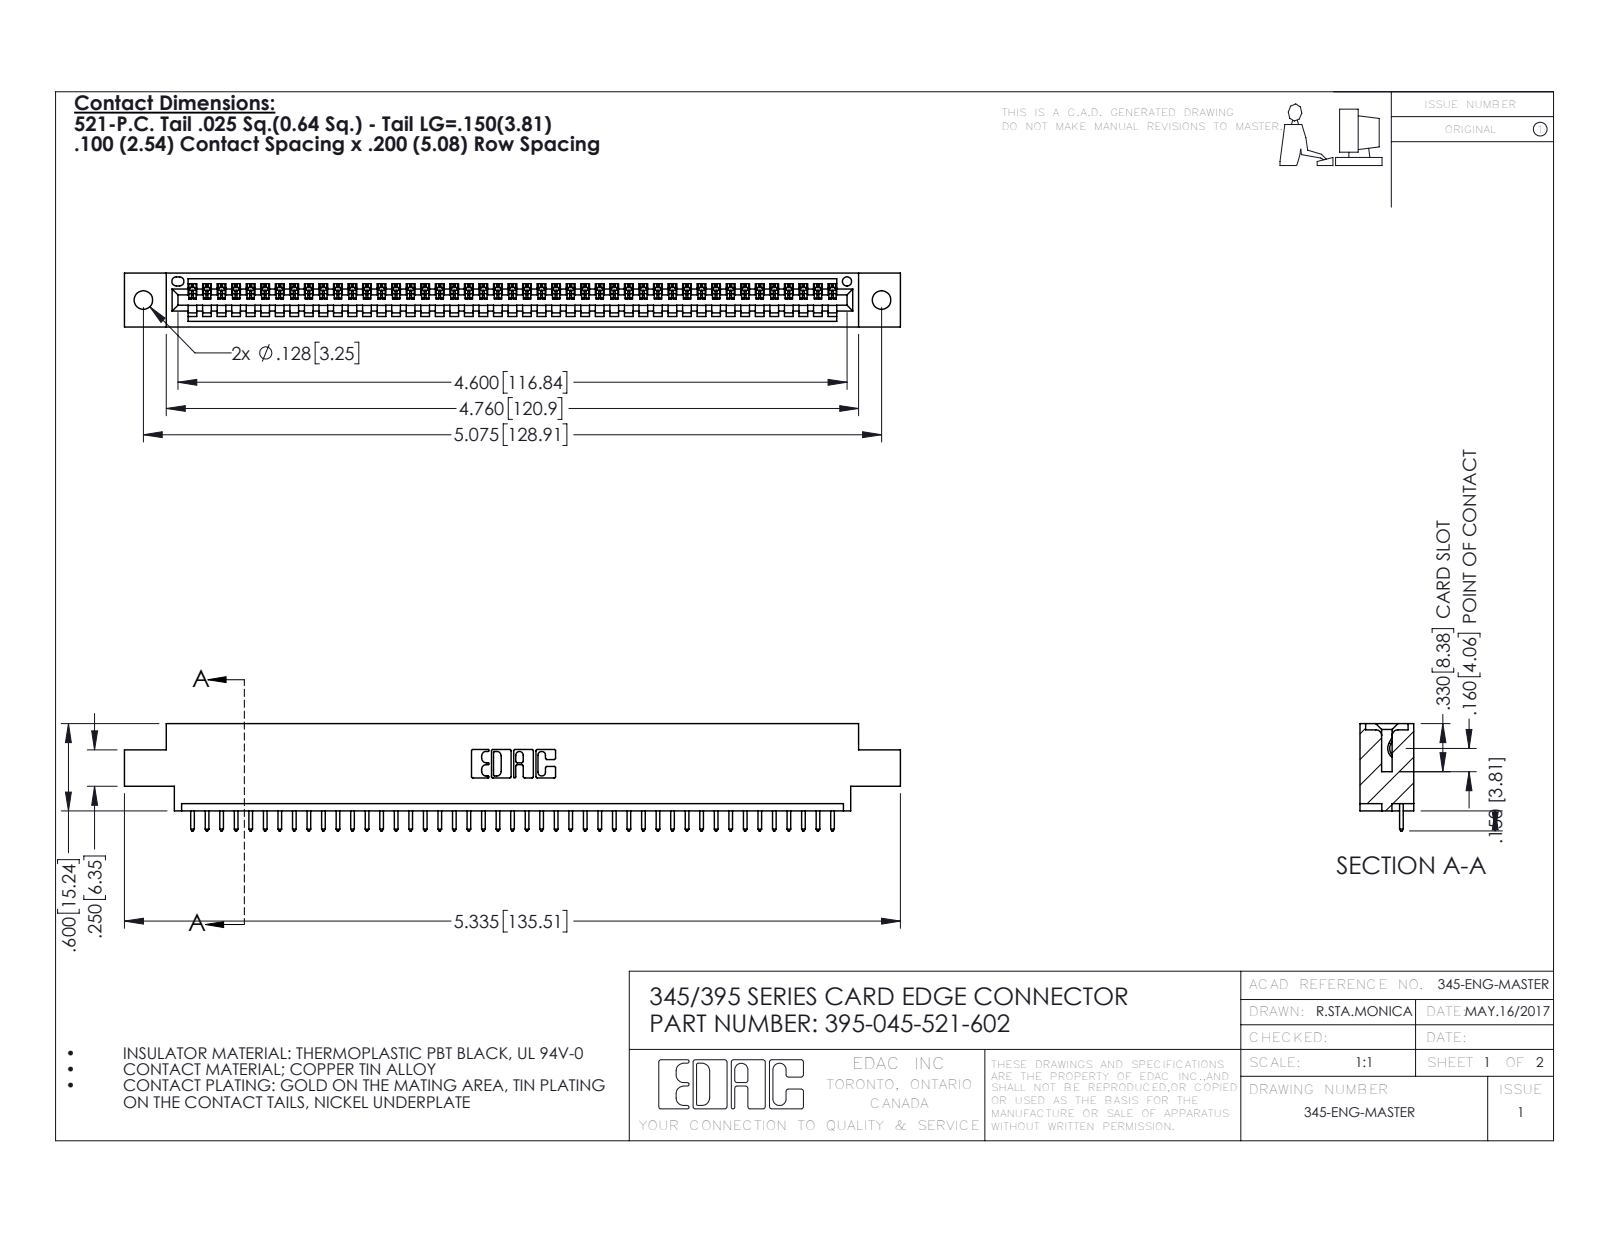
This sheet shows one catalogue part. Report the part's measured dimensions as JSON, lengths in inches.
{"part_name": "395-045-521-602; 345-292-001_345-293-121; 345 Part_0.170 Offset - 0.128 Dia", "step_written_by": "SolidWorks 2016 (CONFIG_CONTROL_DESIGN)", "units": "inches", "bodies": {"solids": 46, "faces": 2740, "planar": 1884, "cylindrical": 856, "other": 0}, "overall_size": [5.335, 0.737, 0.37], "volume_in3": 0.77, "surface_area_in2": 25.05, "round_holes": [[0.128, 2], [0.064, 1]], "partial_cylinders_radius": [[0.006, 90], [0.01, 90], [0.01, 22], [0.007, 6], [0.031, 6], [0.026, 3], [0.031, 2], [0.04, 2]], "face_to_face_distances": [0.298, 0.072, 0.37, 0.2, 0.098, 0.272, 0.025, 0.225, 0.175, 0.149], "hole_center_spacings": [0.27, 4.839, 5.075]}
